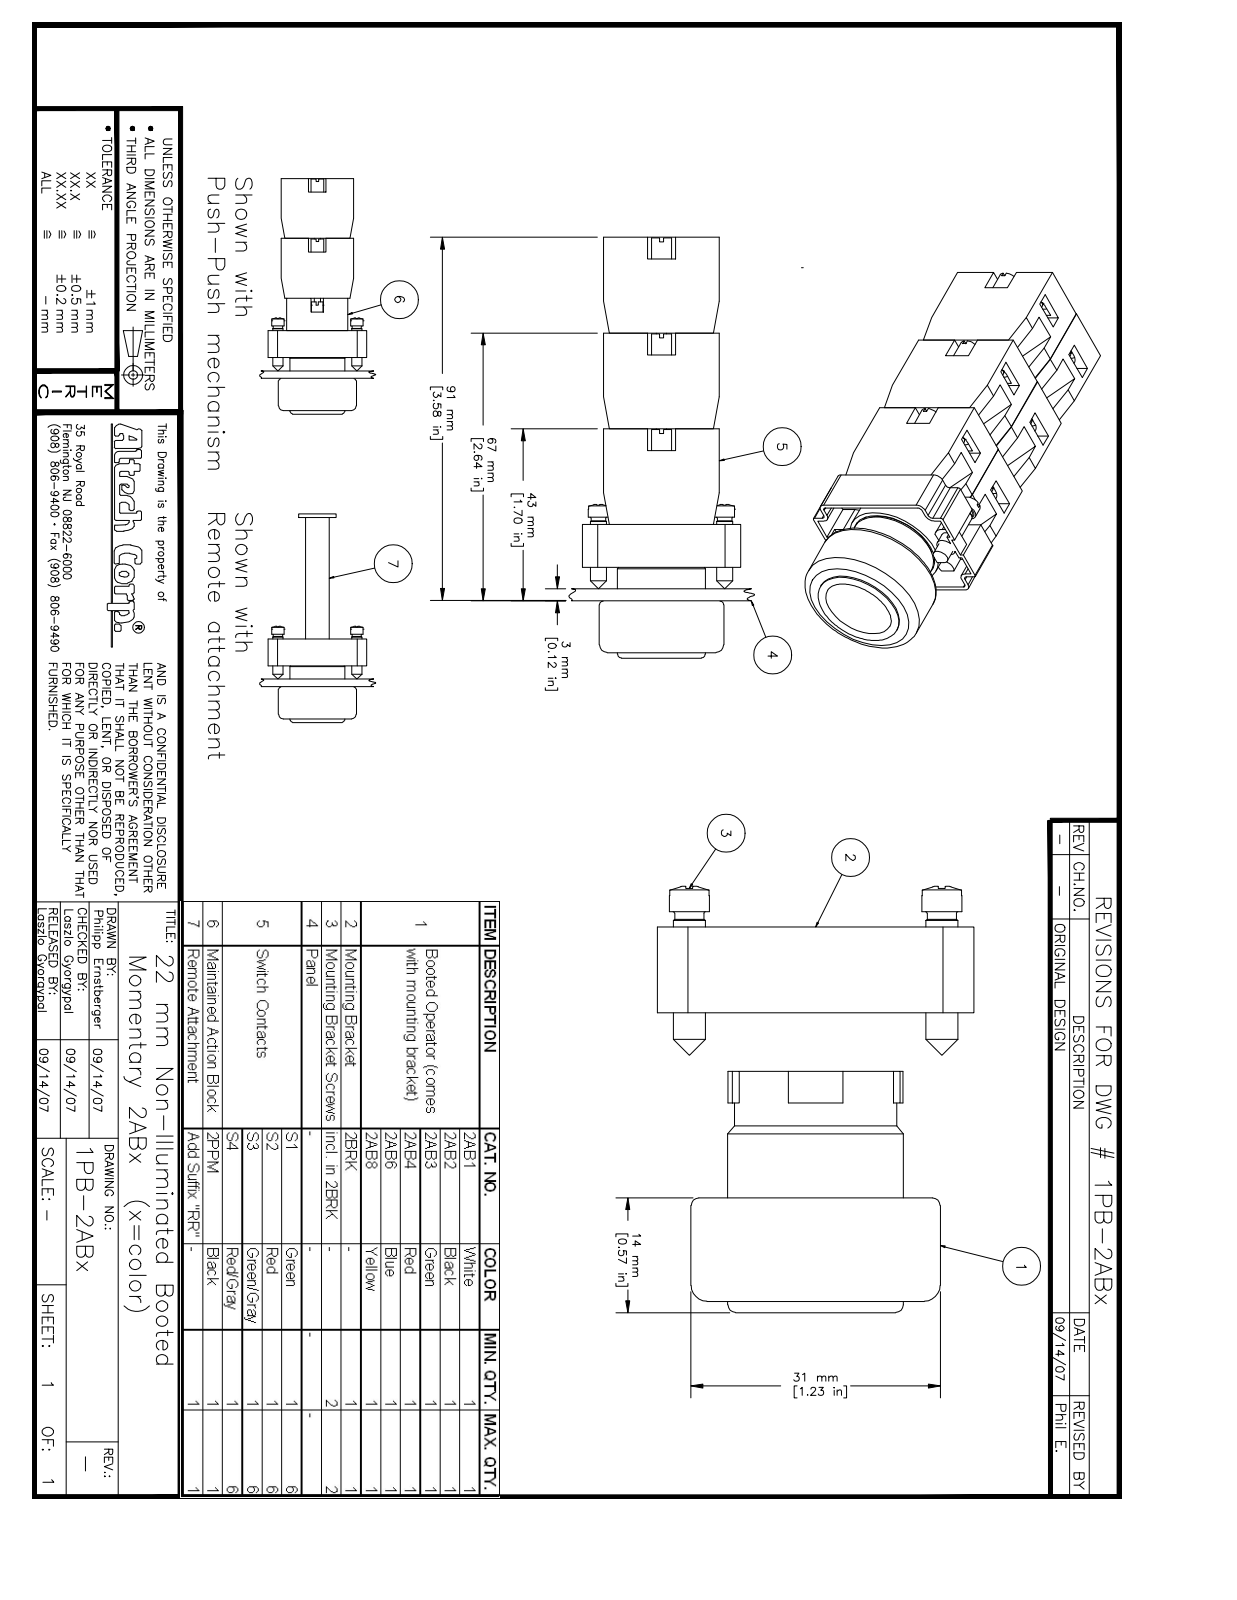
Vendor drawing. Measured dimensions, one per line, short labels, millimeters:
name: 2ABx_mounting_bracket; 2ABx; 2BRK; DIN 7985 (Z) M4x18-Z
written by: Autodesk Inventor 2008 (AUTOMOTIVE_DESIGN)
unit: mm
bodies: 4 solids, 259 faces (131 planar, 80 cylindrical, 48 other)
size: 39.97 × 38.55 × 31.2
volume: 16 022 mm³; area: 12 005 mm²
holes: 5× ⌀2.5, 1× ⌀13.5, 1× ⌀18, 1× ⌀22.25, 1× ⌀26.2
bosses: 2× ⌀5, 2× ⌀4, 2× ⌀3.65, 1× ⌀31.2, 1× ⌀24.25, 1× ⌀22, 1× ⌀20.3, 1× ⌀15
rounds: 10× R0.25, 8× R0.72, 5× R2.25, 4× R0.5, 4× R0.8, 4× R1, 4× R1.8, 4× R2
face distances: 1, 29, 30, 19.1, 32.49, 31.49, 38.6, 10.75, 9.75, 21.74
hole spacings: 14.53, 6.52, 13, 26, 26.27, 29.07, 12.45
